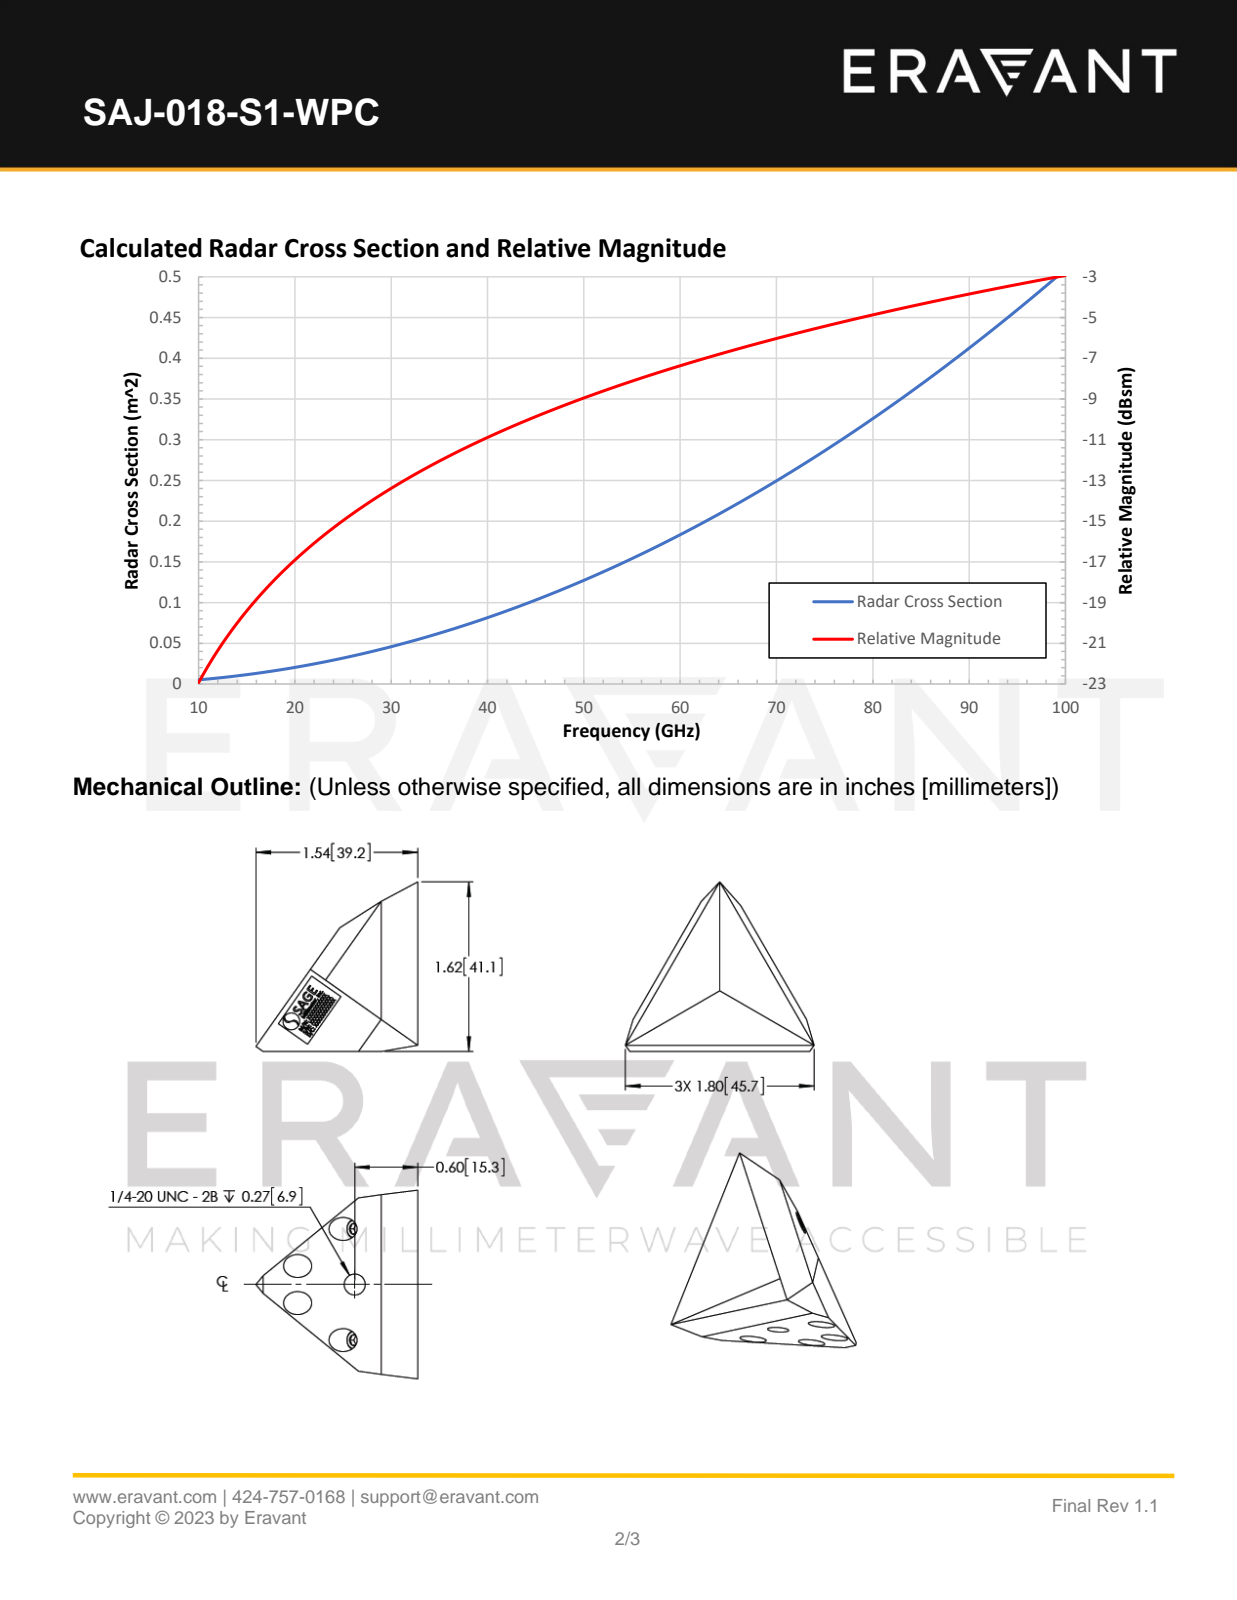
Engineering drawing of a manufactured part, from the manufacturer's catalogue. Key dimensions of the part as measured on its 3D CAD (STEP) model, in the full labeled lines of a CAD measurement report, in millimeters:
Part name (STEP PRODUCT): SAJ-018-S1
STEP written by: SolidWorks 2016 (CONFIG_CONTROL_DESIGN)
Units: millimetres
Bodies: 3 solids, 23 faces (19 planar, 2 cylindrical, 2 other)
Overall size (bounding box): 55.2 × 45.7 × 31.9
Volume: 14 500 mm³ · Surface area: 6 697 mm²
Round holes (diameter × count): ⌀5.1 ×1
Main face-to-face distances: 6.4, 22.9
